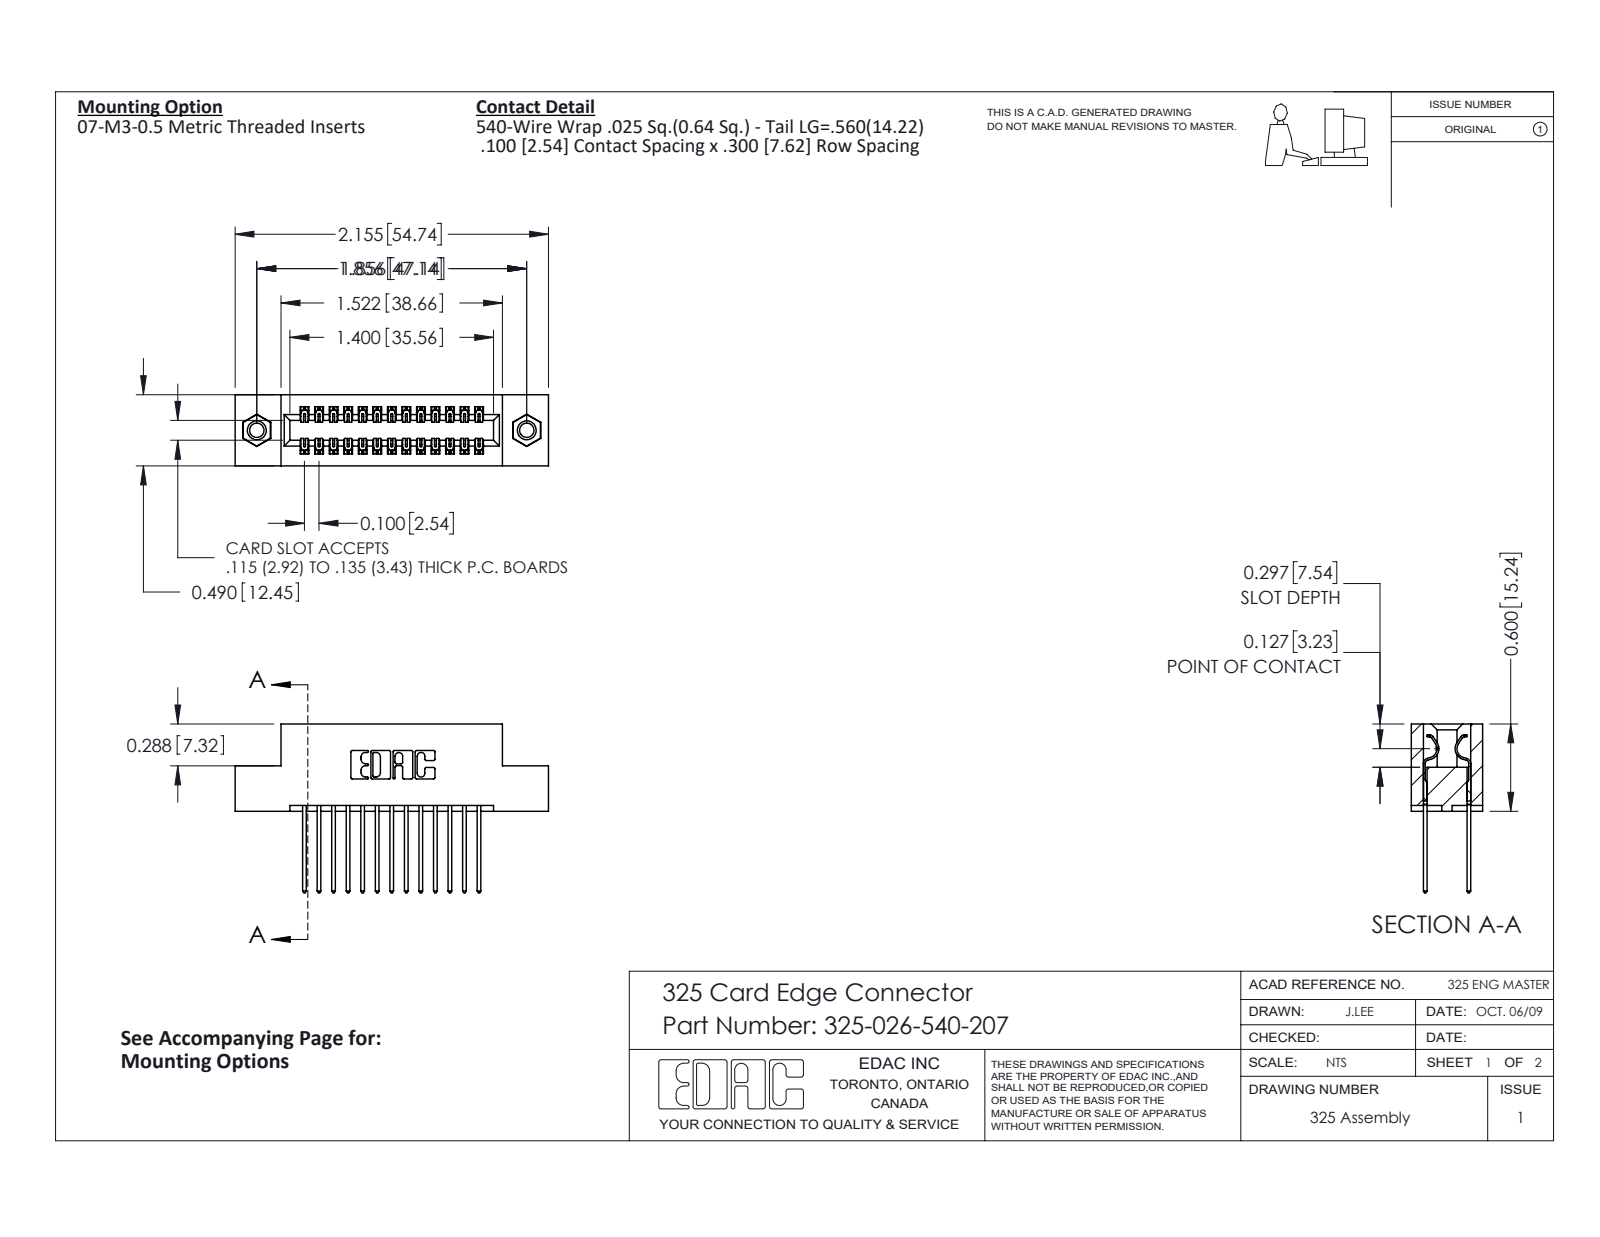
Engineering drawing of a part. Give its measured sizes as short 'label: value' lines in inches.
name: 325-292-001_325-293-140; 345-250-001_345-250-005-103; 325-026-540-207; 325 Part_TI
written by: SolidWorks 2016 (CONFIG_CONTROL_DESIGN)
unit: in
bodies: 29 solids, 1526 faces (1038 planar, 472 cylindrical, 16 other)
size: 2.155 × 1.16 × 0.49
volume: 0.421 in³; area: 12.63 in²
holes: 2× ⌀0.098, 2× ⌀0.125, 2× ⌀0.16
bosses: 2× ⌀0.155
rounds: 39× R0.006, 26× R0.01, 22× R0.01, 6× R0.007, 6× R0.031, 3× R0.026, 2× R0.014, 2× R0.022
face distances: 0.083, 0.407, 0.3, 0.49, 0.107, 0.383, 0.025, 0.325, 0.04, 0.1
hole spacings: 1.856
